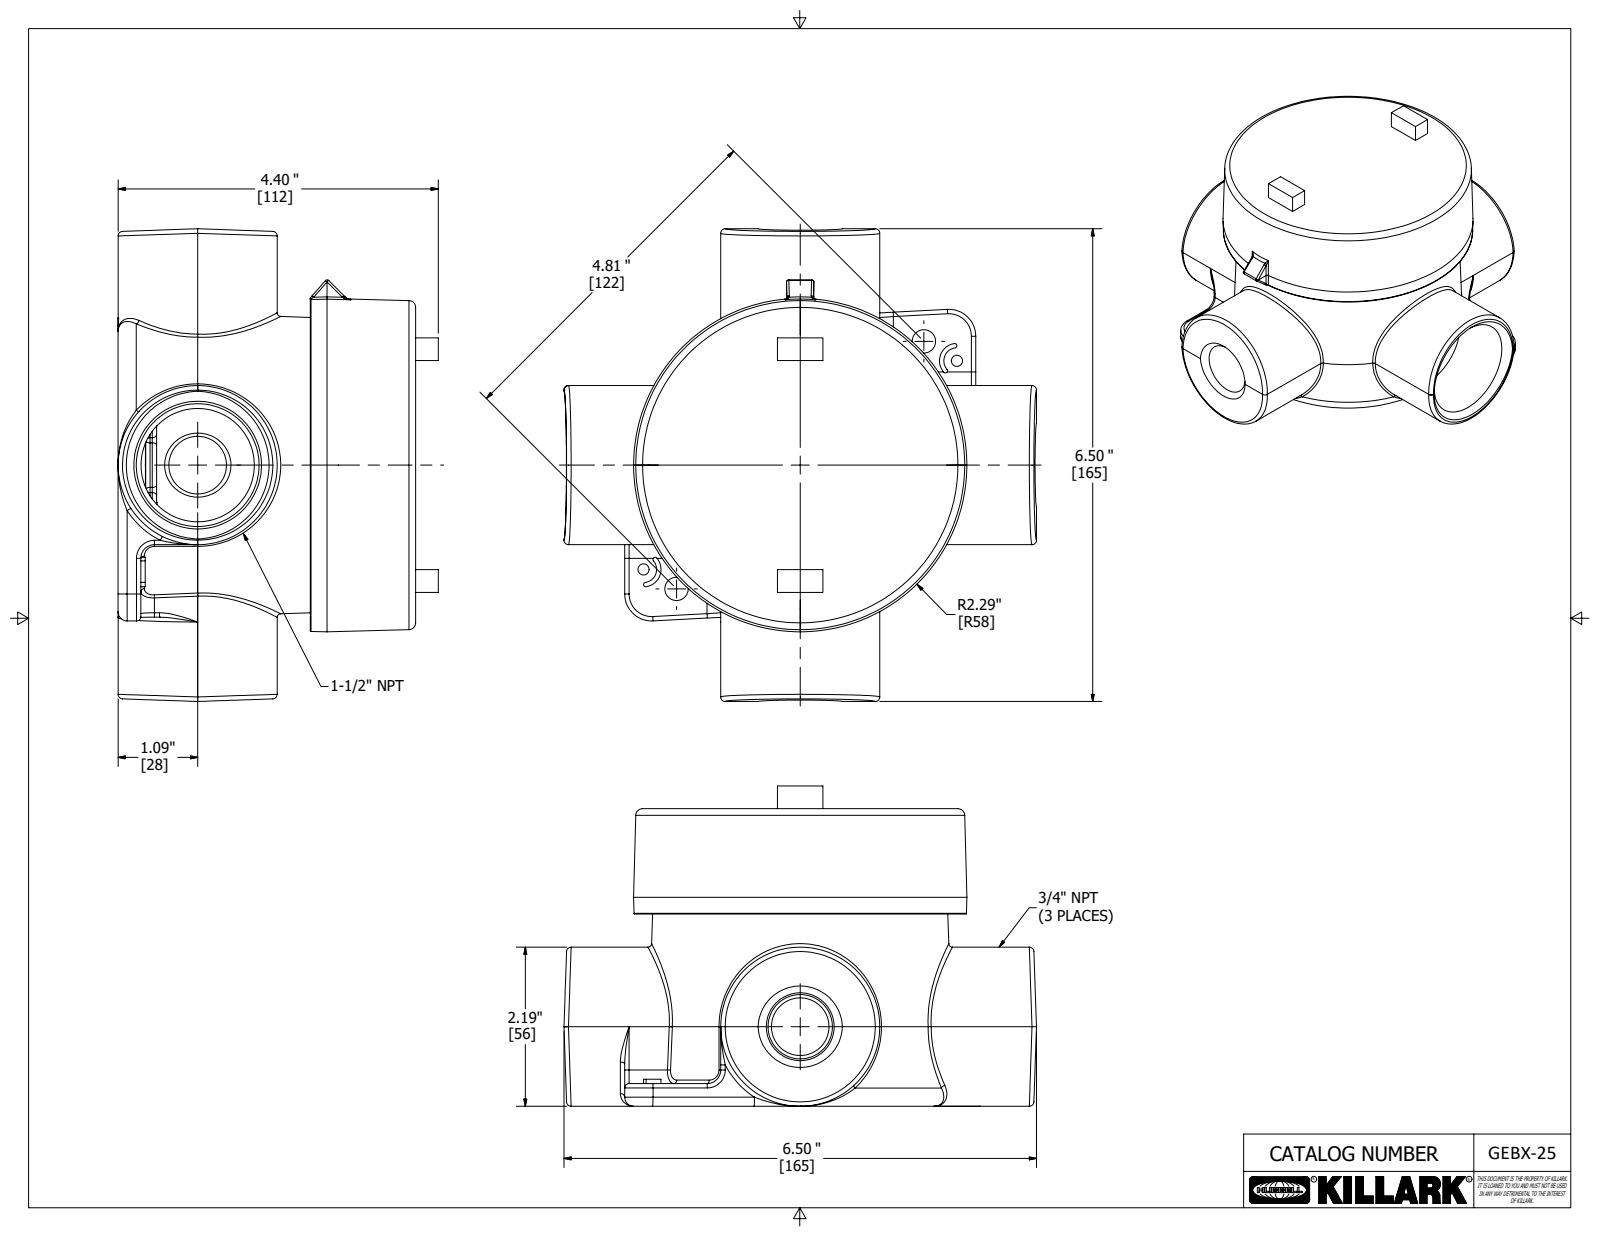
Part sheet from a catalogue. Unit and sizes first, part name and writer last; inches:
Units: inches
Overall size (bounding box): 6.5 × 6.5 × 4.405
Round holes (diameter × count): ⌀0.153 ×2, ⌀0.321 ×2, ⌀0.792 ×2, ⌀1.558 ×1, ⌀3.823 ×1, ⌀4.045 ×1
Round bosses / shafts (diameter × count): ⌀2.188 ×2
Partial cylindrical surfaces — rounded edges, fillets, slot ends (radius × count): R0.06 ×36, R0.03 ×14, R0.125 ×4, R0.187 ×4, R0.031 ×3, R0.18 ×2, R0.24 ×2, R0.37 ×2
Main face-to-face distances: 4.093, 3.655, 0.437, 3.5, 0.155, 0.593, 2.644, 0.856, 1.011, 1.449
Hole centre spacings: 0.527, 2.406, 2.589, 4.97, 4.812, 5.178
Volume: 43.58 in³ · Surface area: 223.2 in²
Bodies: 2 solids, 918 faces (418 planar, 98 cylindrical, 402 other)
Part name (STEP PRODUCT): GEBX-25; 24965-1; 21147-override
STEP written by: Autodesk Inventor 2020 (AUTOMOTIVE_DESIGN)
